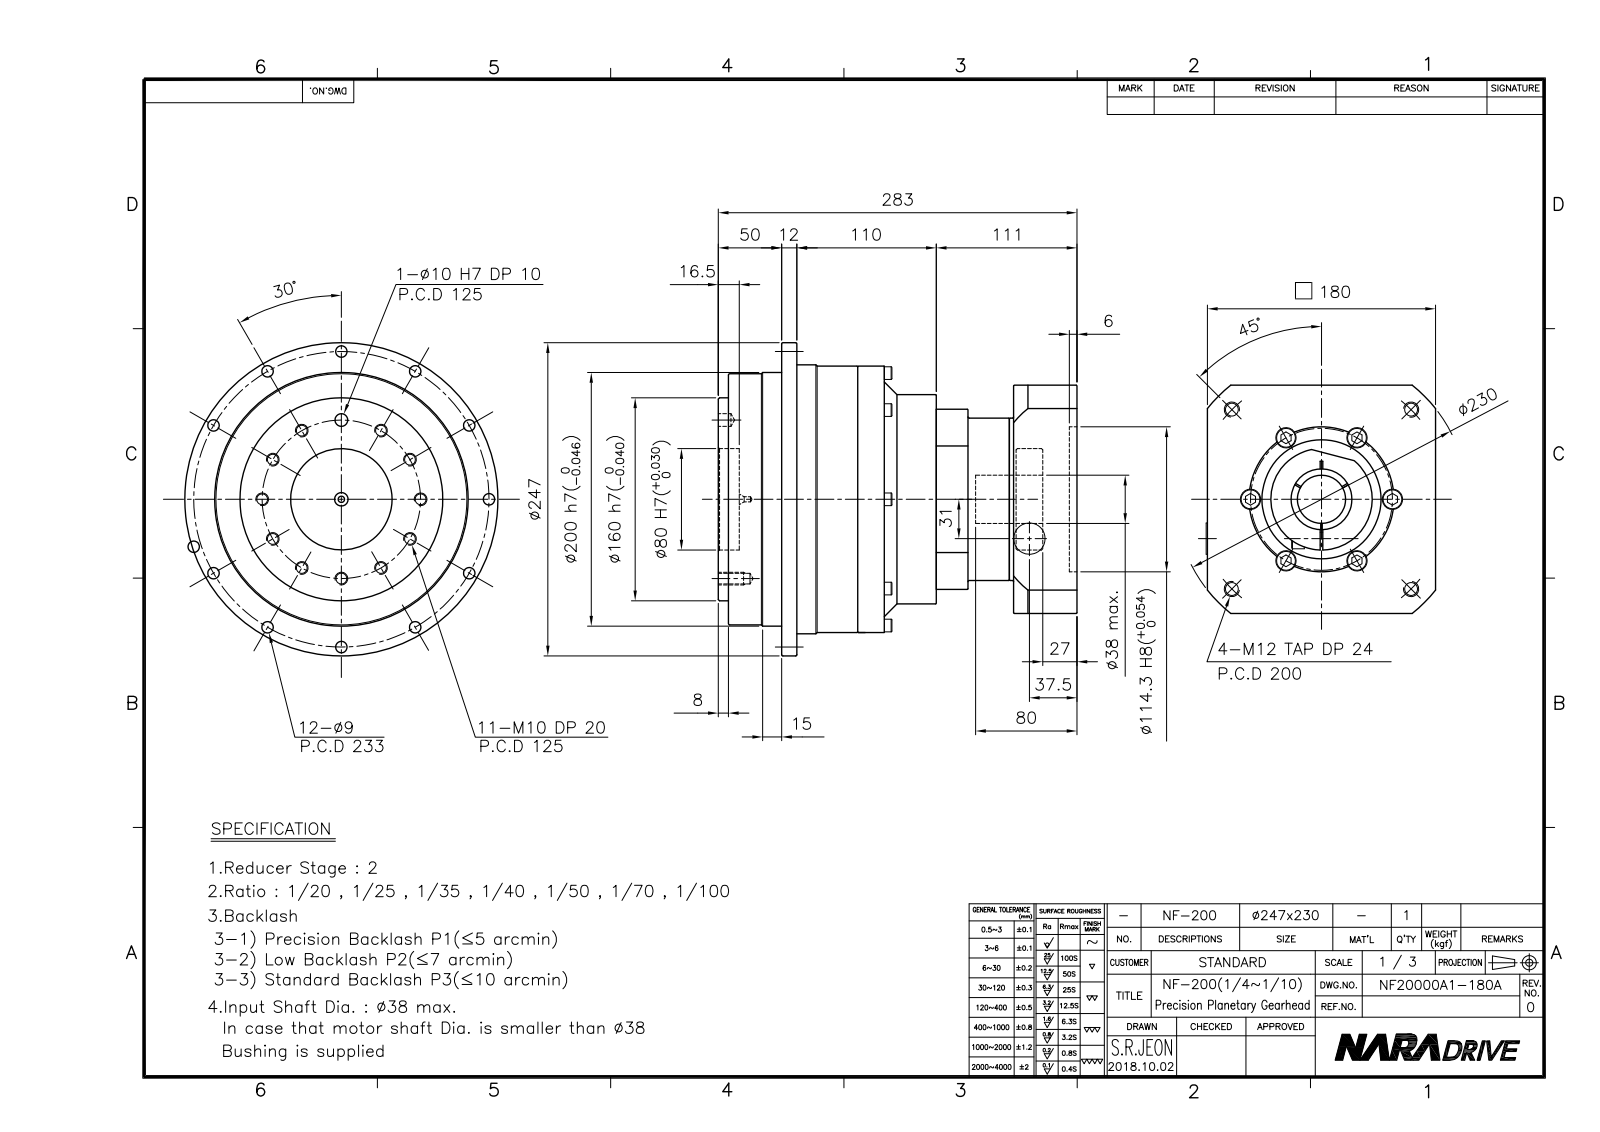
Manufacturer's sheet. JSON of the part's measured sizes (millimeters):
{"part_name": "NF20000A2-180A", "step_written_by": "Autodesk Inventor 2015 (AUTOMOTIVE_DESIGN)", "units": "millimeters", "bodies": {"solids": 2, "faces": 581, "planar": 253, "cylindrical": 172, "other": 156}, "overall_size": [283, 247, 247], "volume_mm3": 5717000, "surface_area_mm2": 526301, "round_holes": [[9, 18], [8.38, 12], [6.65, 10], [14, 10], [4.92, 8], [6.6, 8], [8.5, 4], [10.11, 4], [10, 1], [11, 1], [12.5, 1], [14.5, 1]], "round_bosses_or_shafts": [[10, 9], [6, 8], [13, 6], [8, 6], [247, 1], [212, 1], [210, 1], [200, 1]], "partial_cylinders_radius": [[0.5, 8], [5.5, 8], [1, 4], [9, 1], [57.15, 1], [115, 1]], "face_to_face_distances": [233, 50, 110, 173, 62, 25, 123, 59, 60, 183], "hole_center_spacings": [116.5, 56, 152.42, 167.36, 60.31, 73.54, 84.24, 100.92]}
